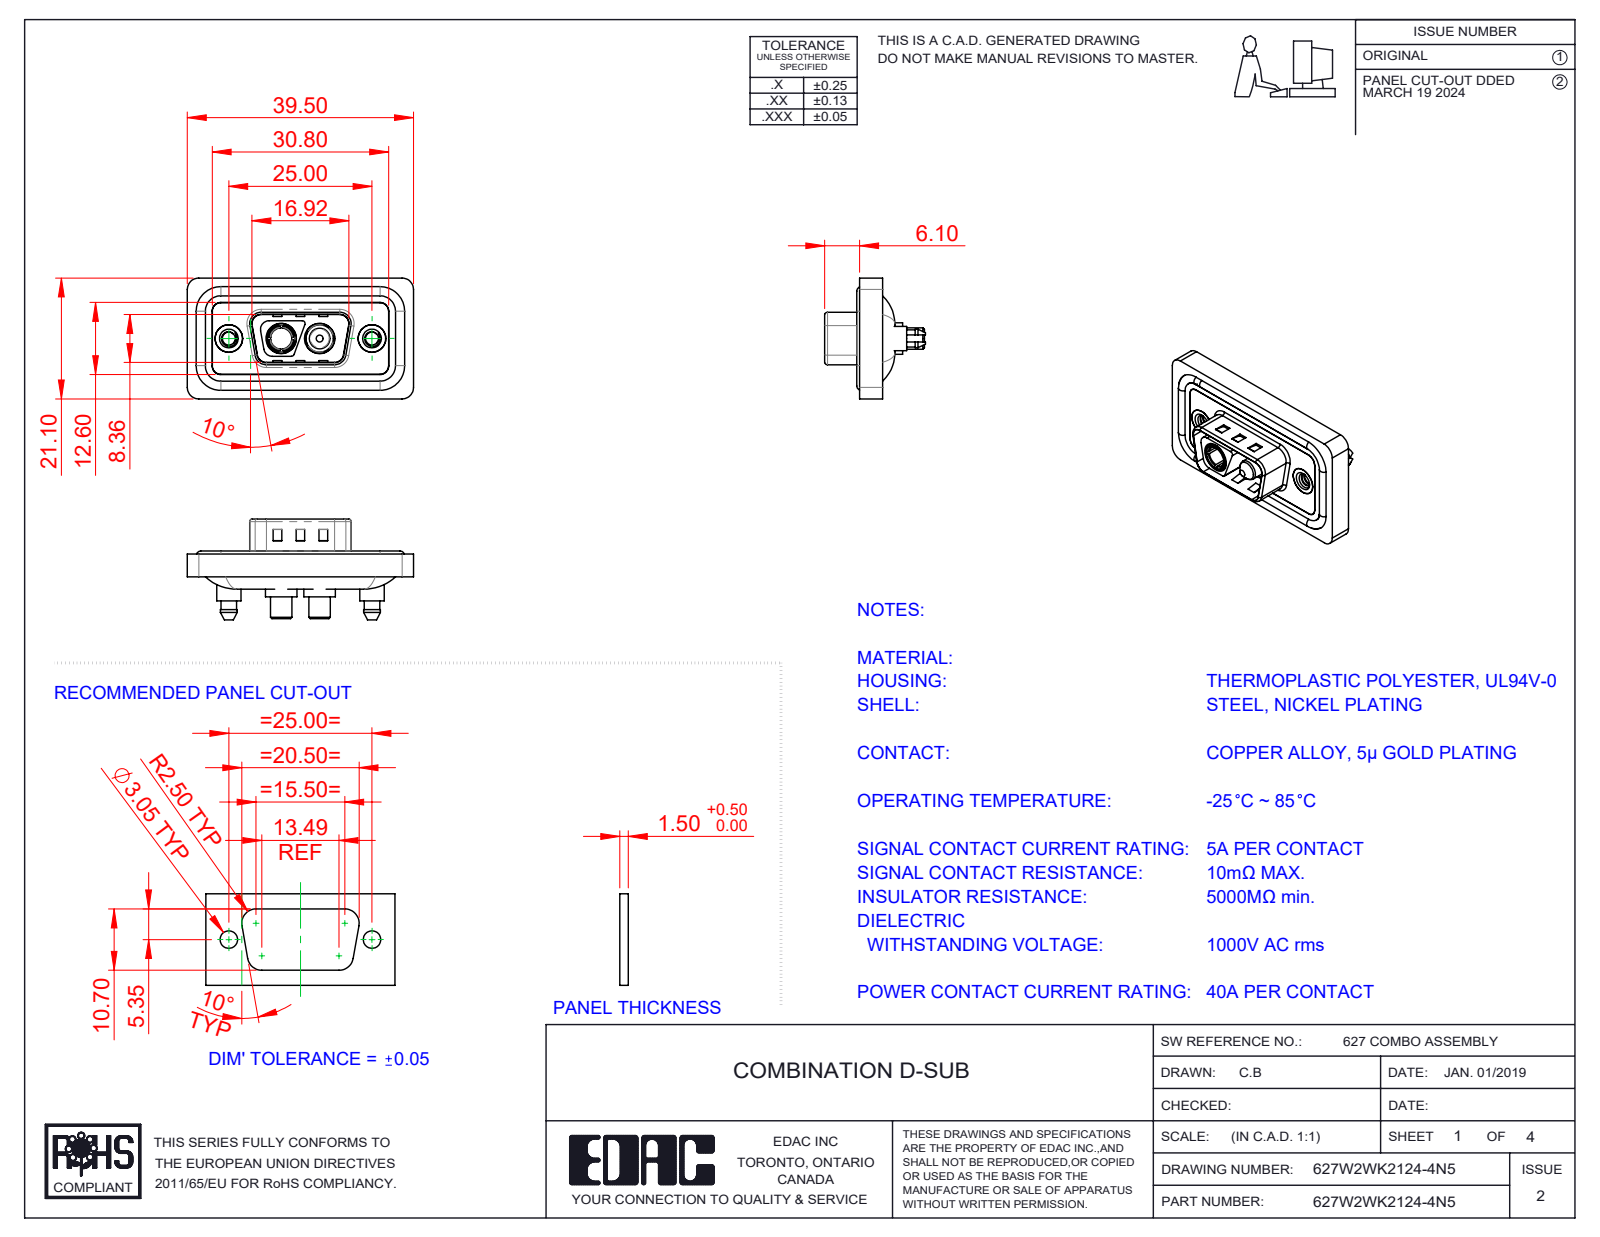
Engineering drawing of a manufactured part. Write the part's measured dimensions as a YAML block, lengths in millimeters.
part_name: "627Combo Waterproof Housing_09 Contacts; 627W2WK2124-4N5; Power Pin_40A S; 627Combo Shell Front_09 Contacts (+4 more)"
step_written_by: "SolidWorks 2023 (CONFIG_CONTROL_DESIGN)"
units: millimeters
bodies: {solids: 11, faces: 584, planar: 205, cylindrical: 259, other: 120}
overall_size: [39.5, 21.1, 17.6]
volume: 4725
surface_area: 7697
round_holes:
  - {diameter: 2.26, count: 2}
  - {diameter: 4, count: 2}
  - {diameter: 4.8, count: 2}
  - {diameter: 4.85, count: 2}
  - {diameter: 5, count: 2}
  - {diameter: 5.3, count: 2}
  - {diameter: 3.7, count: 1}
round_bosses_or_shafts:
  - {diameter: 1.6, count: 4}
  - {diameter: 5.5, count: 2}
  - {diameter: 5.4, count: 2}
  - {diameter: 5.2, count: 2}
  - {diameter: 4.9, count: 2}
  - {diameter: 4.75, count: 2}
  - {diameter: 4.25, count: 2}
  - {diameter: 3.75, count: 2}
partial_cylinders:
  - {radius: 1.5, count: 26}
  - {radius: 2, count: 18}
  - {radius: 0.5, count: 10}
  - {radius: 1.6, count: 10}
  - {radius: 0.25, count: 4}
  - {radius: 0.6, count: 4}
  - {radius: 0.65, count: 4}
  - {radius: 0.9, count: 4}
face_to_face_distances: [0.4, 1.1, 2.9, 3.1, 0.5, 1.6, 1.5, 4, 1.8, 3.2]
hole_center_spacings: [9.14, 15.86, 6.72, 25]
